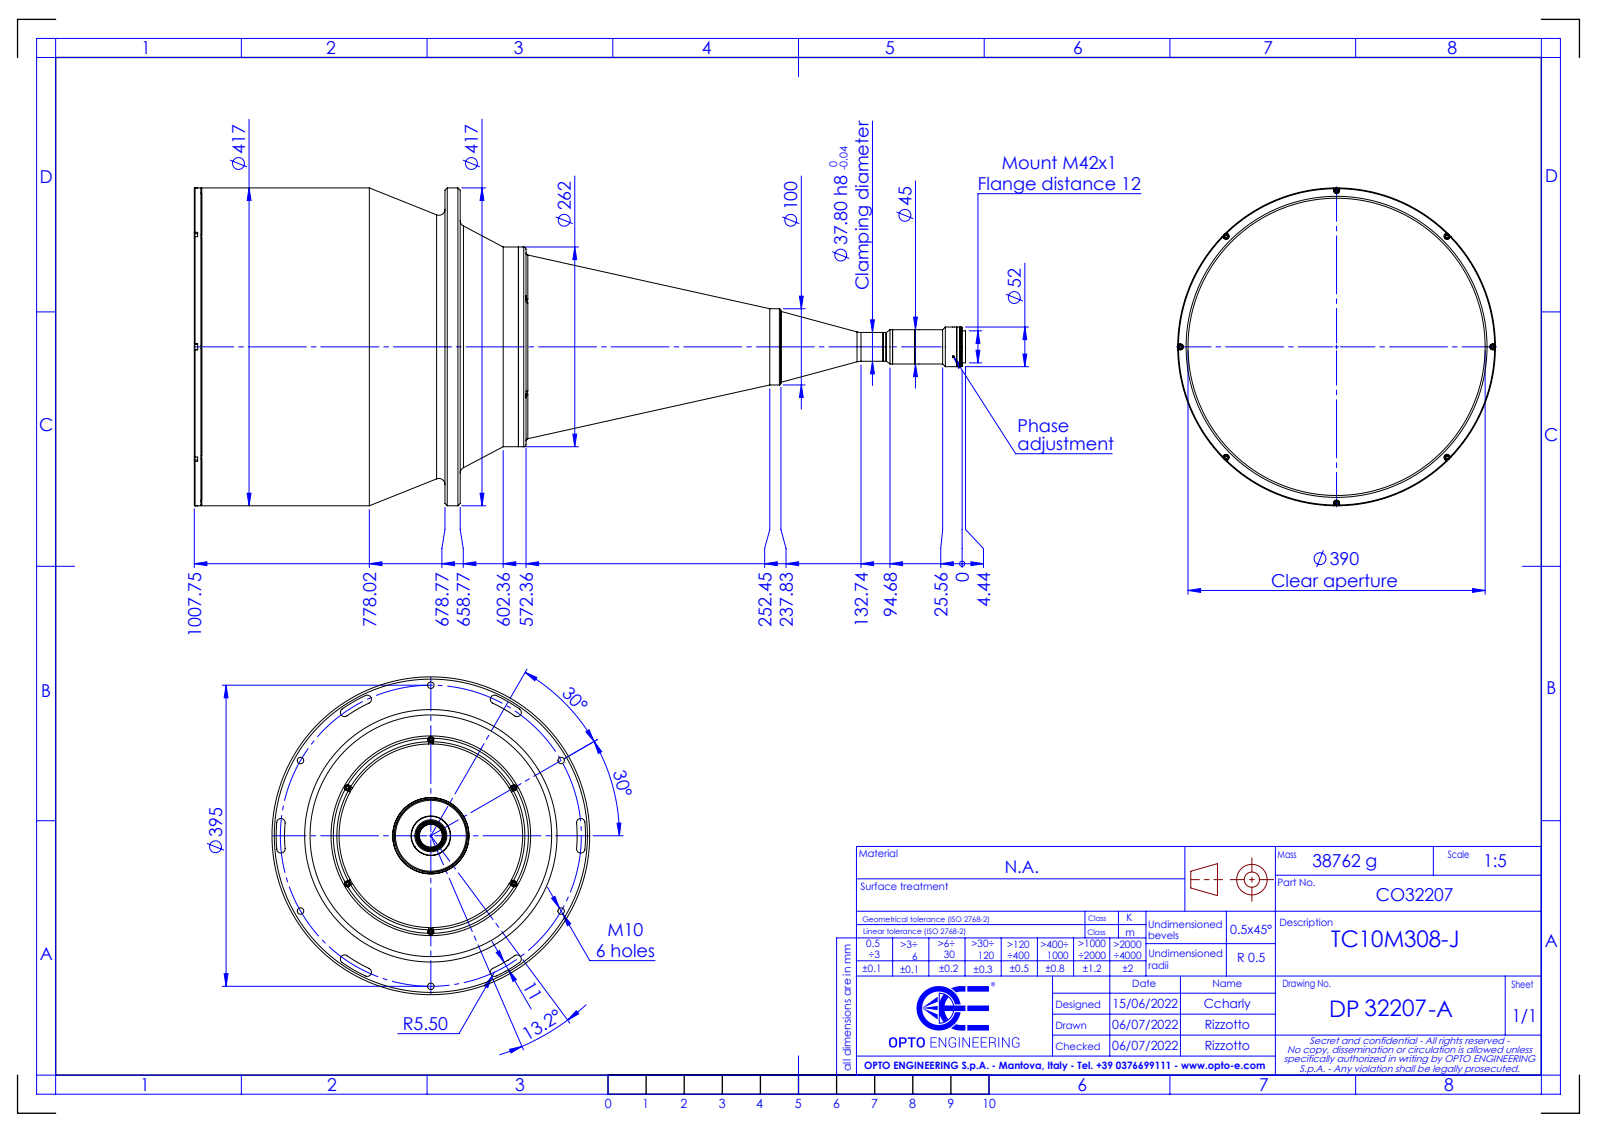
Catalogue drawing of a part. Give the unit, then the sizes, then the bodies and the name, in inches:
Units: inches
Overall size (bounding box): 39.85 × 16.417 × 16.417
Round holes (diameter × count): ⌀0.315 ×6, ⌀0.335 ×6, ⌀0.098 ×3, ⌀1.496 ×1, ⌀15.354 ×1
Round bosses / shafts (diameter × count): ⌀0.276 ×8, ⌀16.417 ×1, ⌀10.315 ×1, ⌀3.937 ×1, ⌀2.047 ×1, ⌀2.039 ×1, ⌀1.772 ×1, ⌀1.654 ×1
Partial cylindrical surfaces — rounded edges, fillets, slot ends (radius × count): R0.217 ×12, R0.157 ×8, R7.559 ×1, R7.992 ×1
Main face-to-face distances: 0.787, 12.952, 13.739, 0.343, 12.609, 13.397, 0.383, 0.041, 12.569, 13.356
Hole centre spacings: 4.961, 6.819, 7.776, 11.119, 2.815, 8.592, 12.736, 13.468
Bodies: 0 solids, 260 faces (60 planar, 127 cylindrical, 73 other)
Part name (STEP PRODUCT): DP32207-A_TC10M308-J
STEP written by: SolidWorks 2021 (CONFIG_CONTROL_DESIGN)
